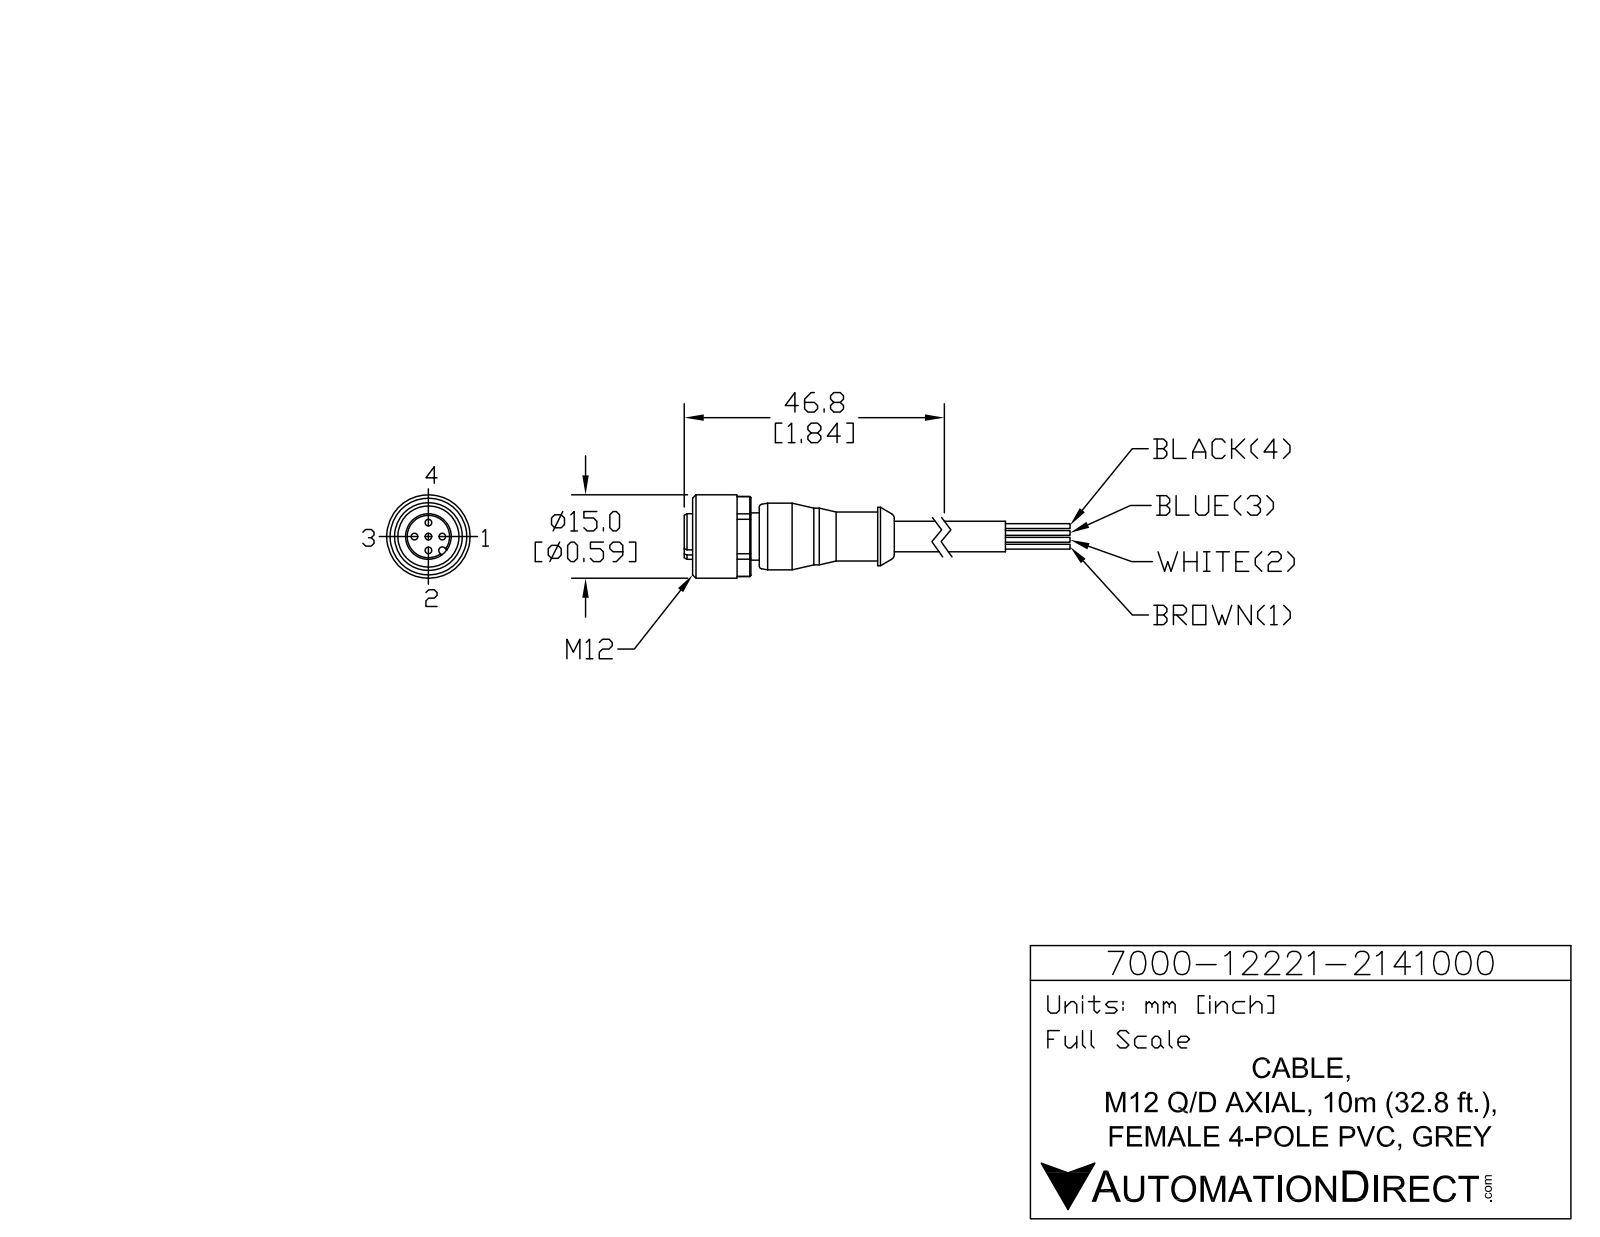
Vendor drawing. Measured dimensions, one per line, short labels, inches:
name: 7000-12221-2141000
written by: SolidWorks 2015 (AUTOMOTIVE_DESIGN)
unit: in
bodies: 1 solid, 93 faces (29 planar, 36 cylindrical, 28 other)
size: 2.276 × 0.591 × 0.591
volume: 0.246 in³; area: 4.134 in²
holes: 5× ⌀0.047, 1× ⌀0.433
bosses: 1× ⌀0.591, 1× ⌀0.472, 1× ⌀0.413, 1× ⌀0.402, 1× ⌀0.346, 1× ⌀0.335, 1× ⌀0.323, 1× ⌀0.217
rounds: 1× R0.026, 1× R0.283
face distances: 0.472, 0.059, 0.118, 0.512, 0.354, 1.016, 0.295, 0.413, 0.098, 0.531
hole spacings: 0.098, 0.139, 0.197
